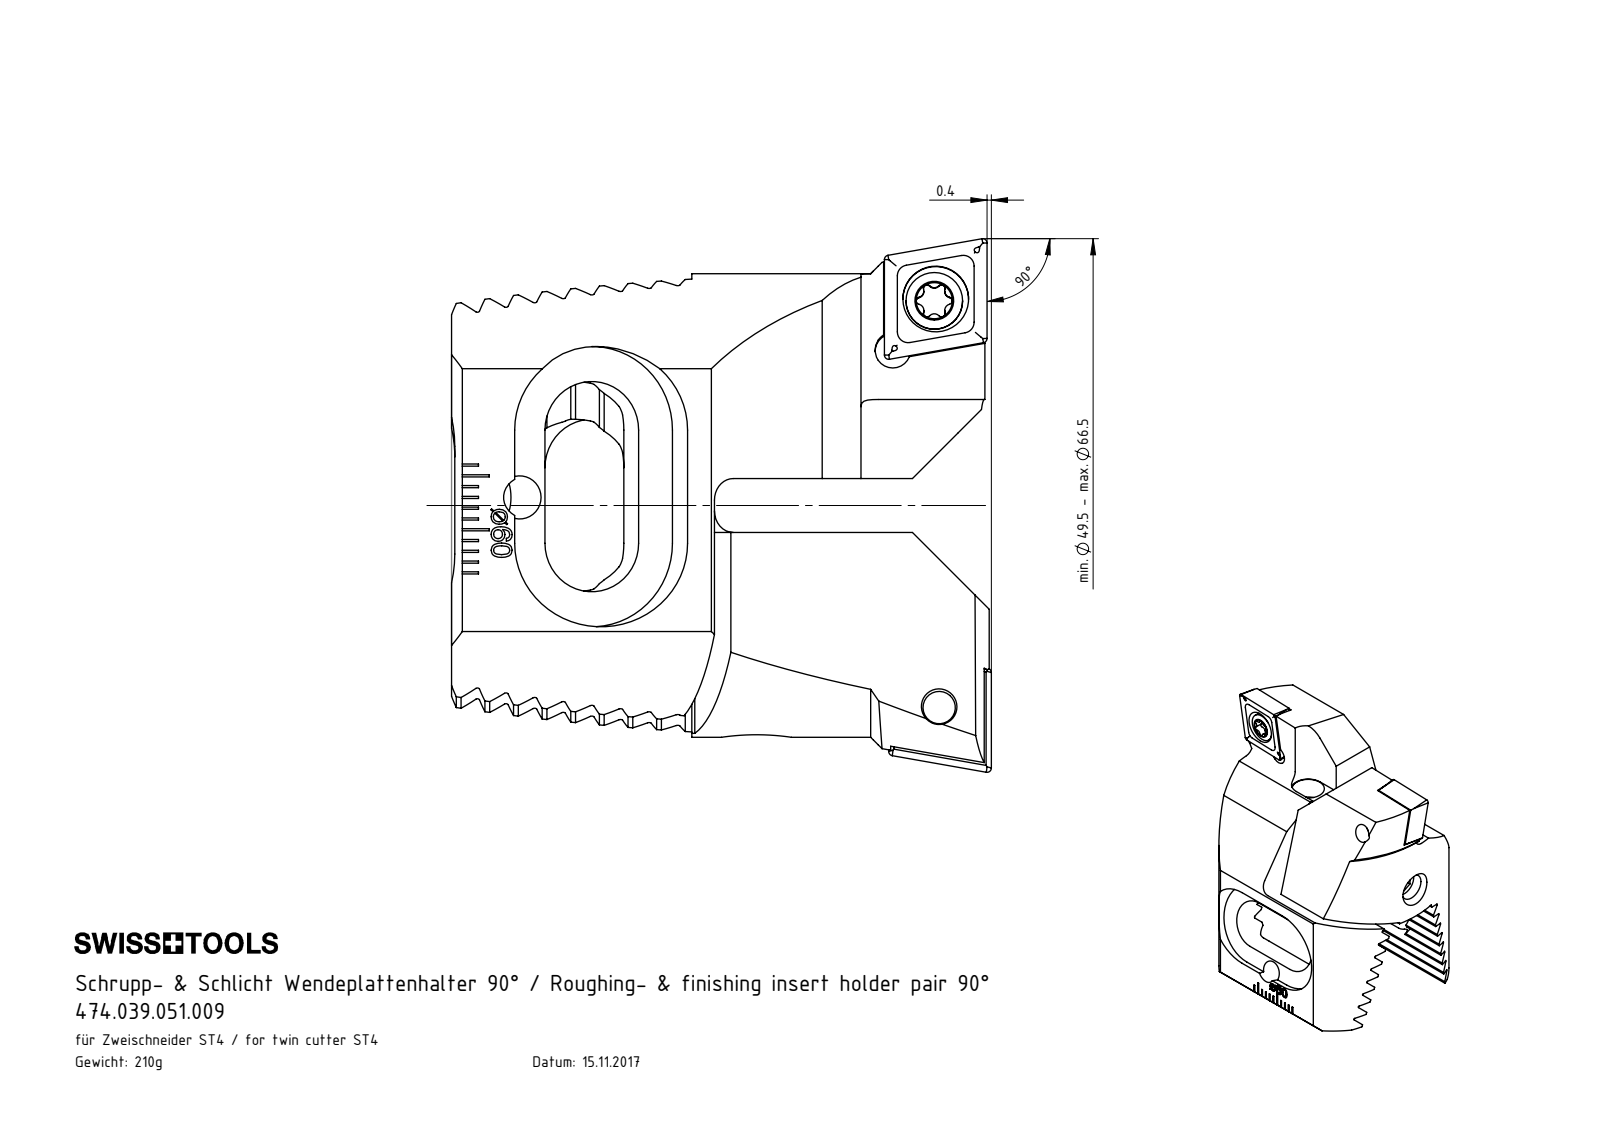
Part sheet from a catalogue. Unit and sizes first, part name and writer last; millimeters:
Units: millimetres
Overall size (bounding box): 50.1 × 49.5 × 34.2
Round holes (diameter × count): ⌀3.3 ×4, ⌀4.4 ×2, ⌀6.1 ×2, ⌀1.6 ×1, ⌀2.5 ×1, ⌀4 ×1, ⌀5 ×1, ⌀6 ×1
Round bosses / shafts (diameter × count): ⌀4 ×3, ⌀5.25 ×2, ⌀6 ×1, ⌀3 ×1, ⌀2 ×1
Partial cylindrical surfaces — rounded edges, fillets, slot ends (radius × count): R0.2 ×16, R0.34 ×12, R0.59 ×12, R2 ×4, R4.5 ×4, R7.75 ×4, R12 ×4, R21 ×4
Main face-to-face distances: 2.38, 4.76, 11.91, 9.53, 14.29, 7.15, 5.5, 4.77, 7.14, 0.5
Hole centre spacings: 6.19, 33.71, 5.99, 6.07, 12, 28.78, 33.55, 33.81
Volume: 26 842 mm³ · Surface area: 13 156 mm²
Bodies: 8 solids, 657 faces (343 planar, 132 cylindrical, 182 other)
Part name (STEP PRODUCT): ISO 4028 - M3 x 5_M3x8; ZC4-xxx.001.028_A_versetzt mit FV; Z42-ER3.001.016; CCMT09T304 (+3 more)
STEP written by: SolidWorks 2017 (CONFIG_CONTROL_DESIGN)
